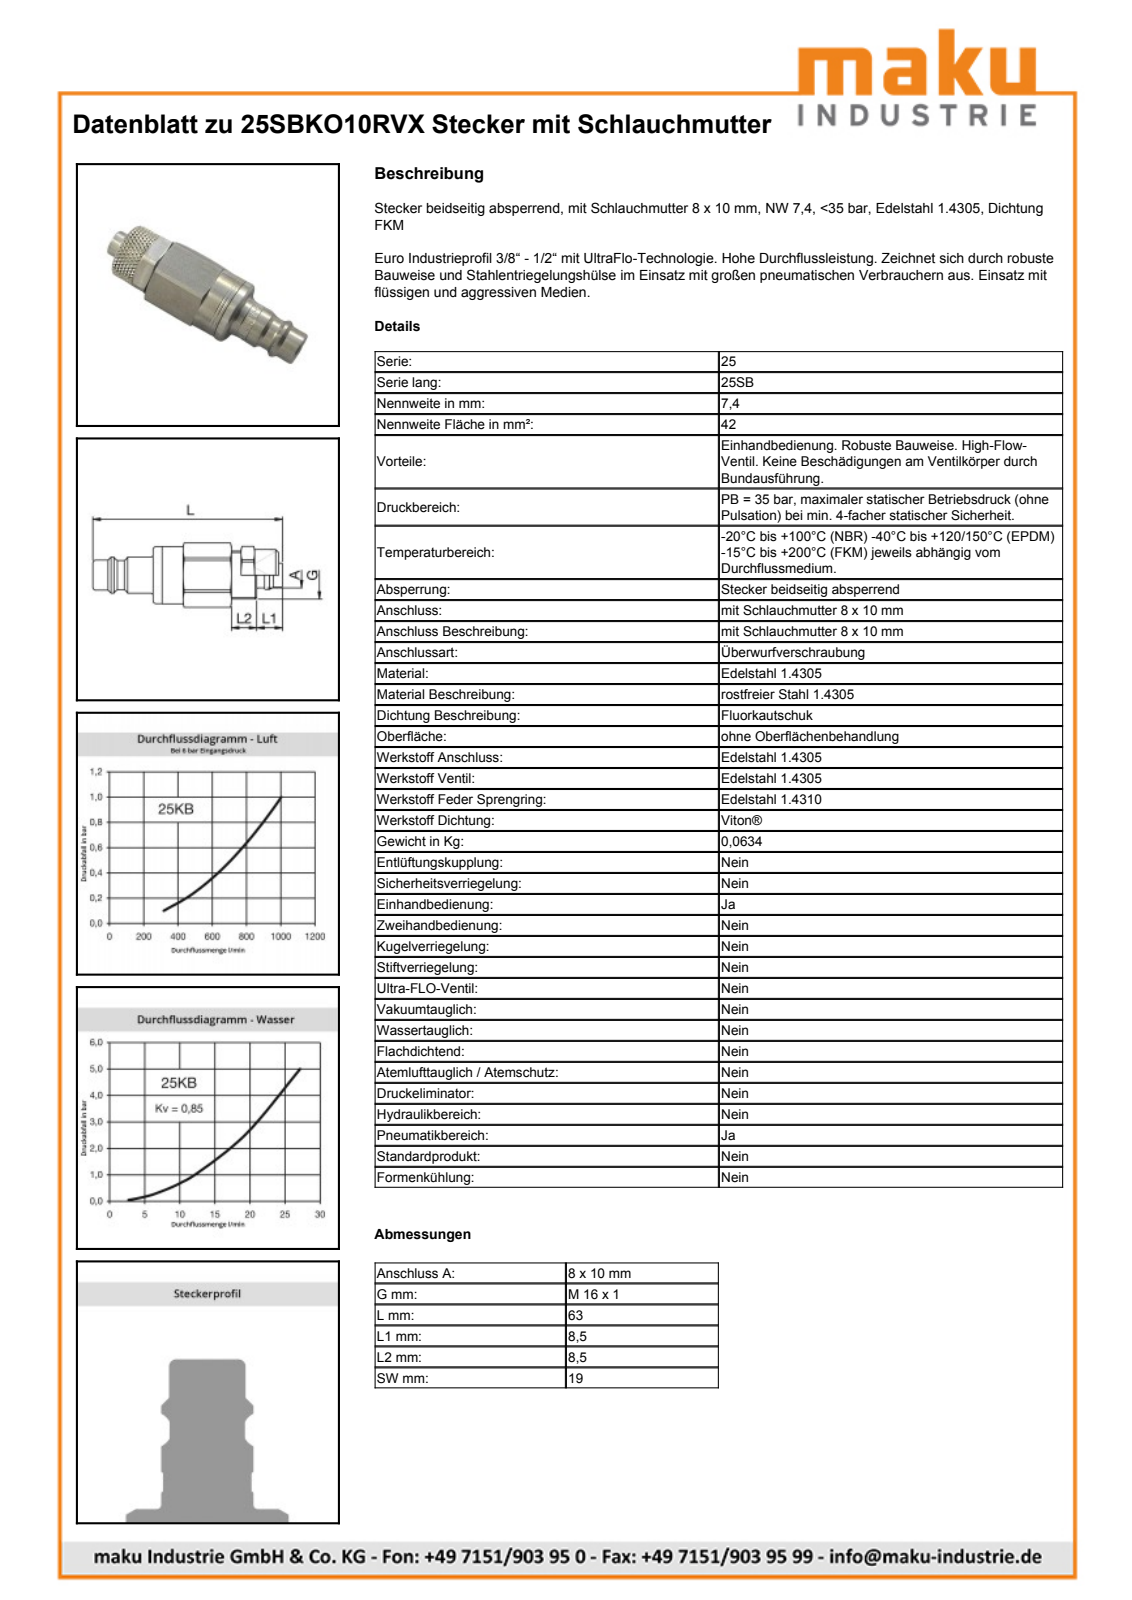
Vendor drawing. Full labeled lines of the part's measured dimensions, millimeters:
Part name (STEP PRODUCT): D105954
STEP written by: Autodesk Inventor 2011 (AUTOMOTIVE_DESIGN)
Units: millimetres
Bodies: 1 solid, 94 faces (26 planar, 30 cylindrical, 38 other)
Overall size (bounding box): 63 × 21.35 × 19.98
Volume: 12 399 mm³ · Surface area: 5 215 mm²
Round holes (diameter × count): ⌀10.2 ×1, ⌀15.1 ×1, ⌀15.6 ×1, ⌀16 ×1
Round bosses / shafts (diameter × count): ⌀19 ×1, ⌀18.95 ×1, ⌀17 ×1, ⌀14.68 ×1, ⌀12 ×1, ⌀9.9 ×1, ⌀9.75 ×1, ⌀9.5 ×1
Partial cylindrical surfaces — rounded edges, fillets, slot ends (radius × count): R9.4 ×1, R10.7 ×1
Main face-to-face distances: 19, 17, 3.5, 5.5, 2, 8.4, 34.4, 37.9, 39.9, 26
